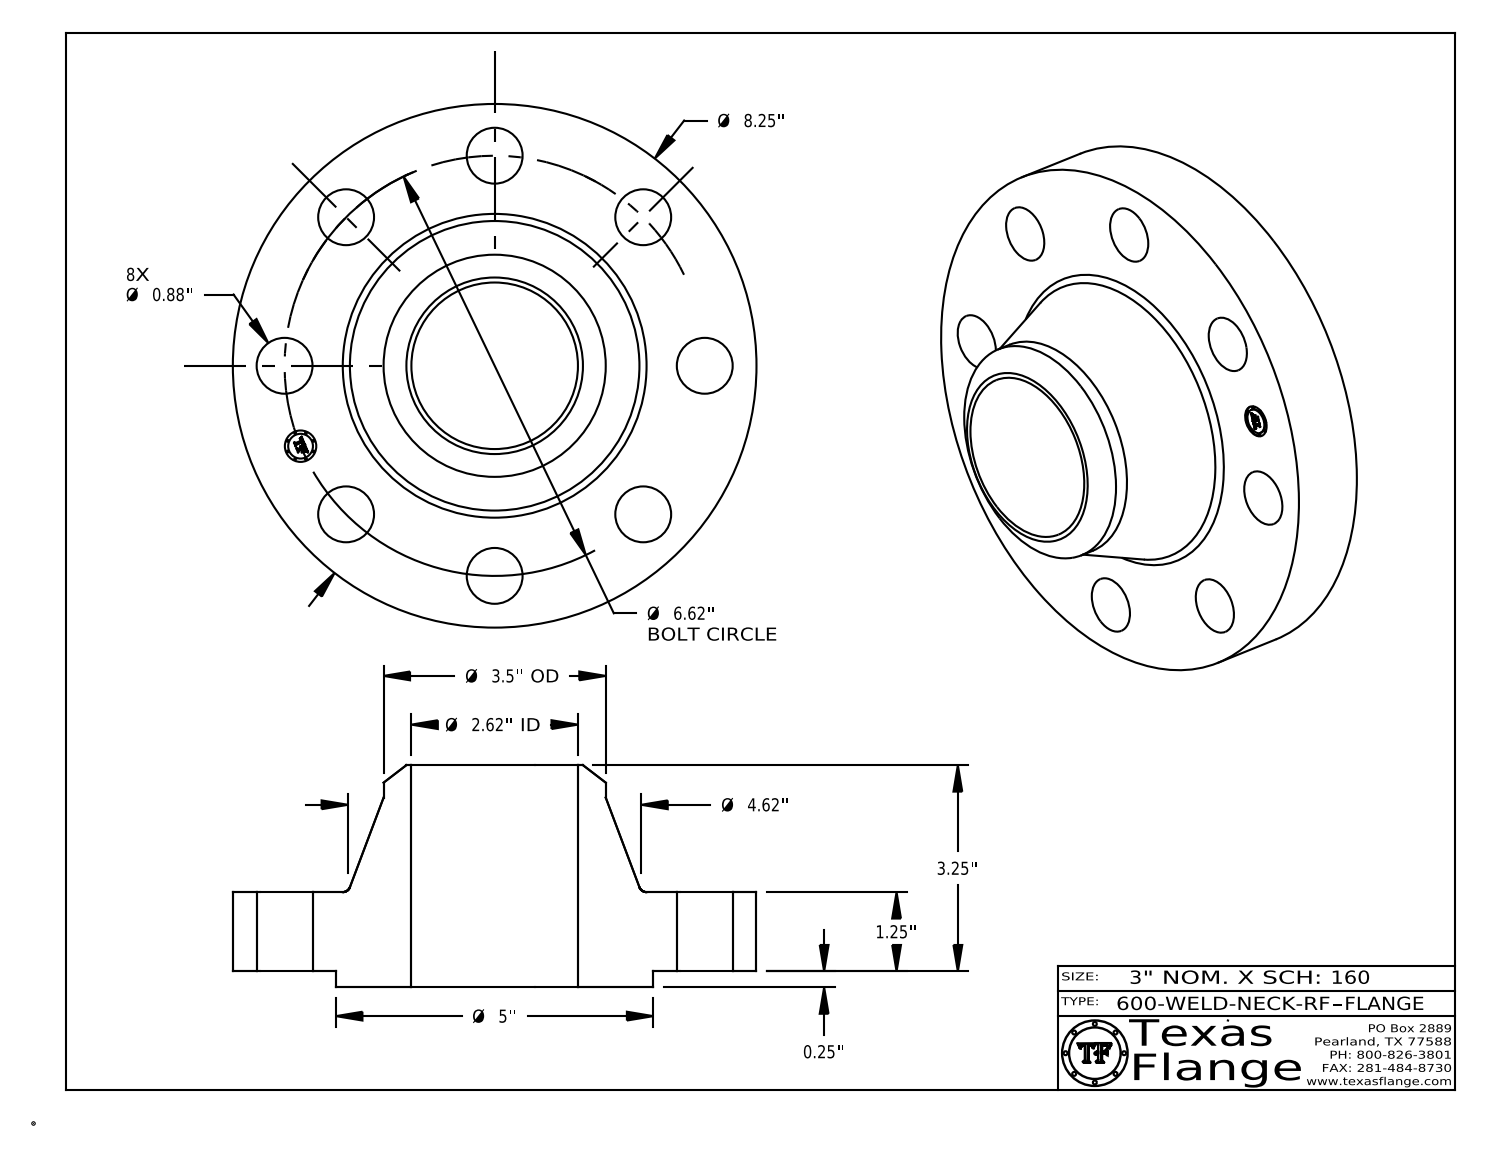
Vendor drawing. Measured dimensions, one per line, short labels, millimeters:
name: 600-WELD-NECK-RF
written by: CATIA V5 STEP AP214 (AUTOMOTIVE_DESIGN)
unit: mm
bodies: 1 solid, 419 faces (369 planar, 44 cylindrical, 6 other)
size: 209.6 × 209.6 × 88.9
volume: 1 156 000 mm³; area: 126 200 mm²
holes: 8× ⌀22.4, 1× ⌀12.6, 1× ⌀66.6
bosses: 8× ⌀0.8, 1× ⌀209.6, 1× ⌀127, 1× ⌀88.9, 1× ⌀9.9
face distances: 31.8, 6.4, 38.1, 88.9, 82.6, 50.8, 0.4, 37.7, 31.4, 51.2
hole spacings: 84.1, 64.3, 155.3, 118.9, 118.9, 32.8, 93.4, 164.9
